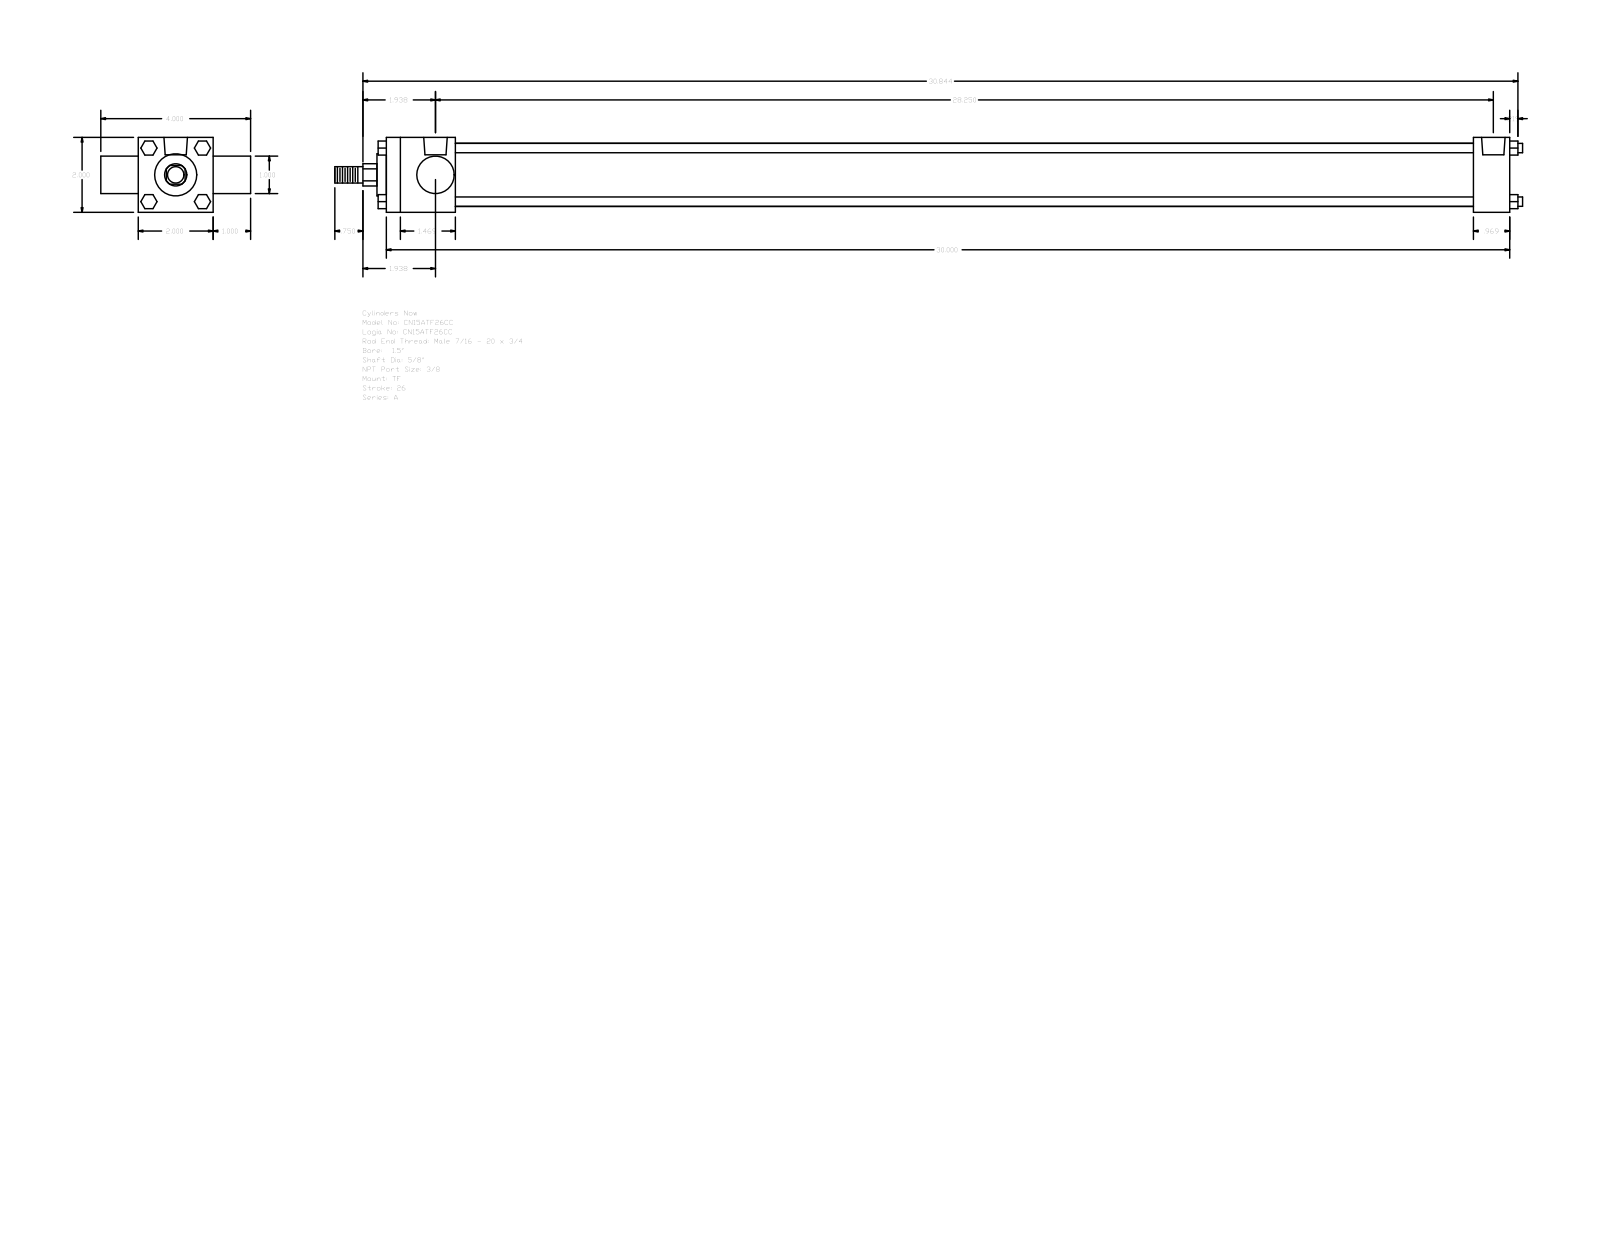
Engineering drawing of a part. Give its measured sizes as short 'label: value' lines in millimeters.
name: A_TF__0150_0.625
written by: GSSL Pune (CONFIG_CONTROL_DESIGN)
unit: mm
bodies: 0 solids, 120 faces (92 planar, 28 cylindrical, 0 other)
size: 805.66 × 101.6 × 50.8
holes: 3× ⌀5.56, 2× ⌀15.93
bosses: 4× ⌀6.35, 1× ⌀42.93, 1× ⌀28.57, 1× ⌀25.4, 1× ⌀15.88, 1× ⌀11.11
rounds: 1× R7.54
face distances: 50.8, 762, 25.4, 76.2, 46.83, 737.39, 690.56, 715.17, 24.61, 101.6
hole spacings: 3.97, 713.58, 709.61, 717.55
